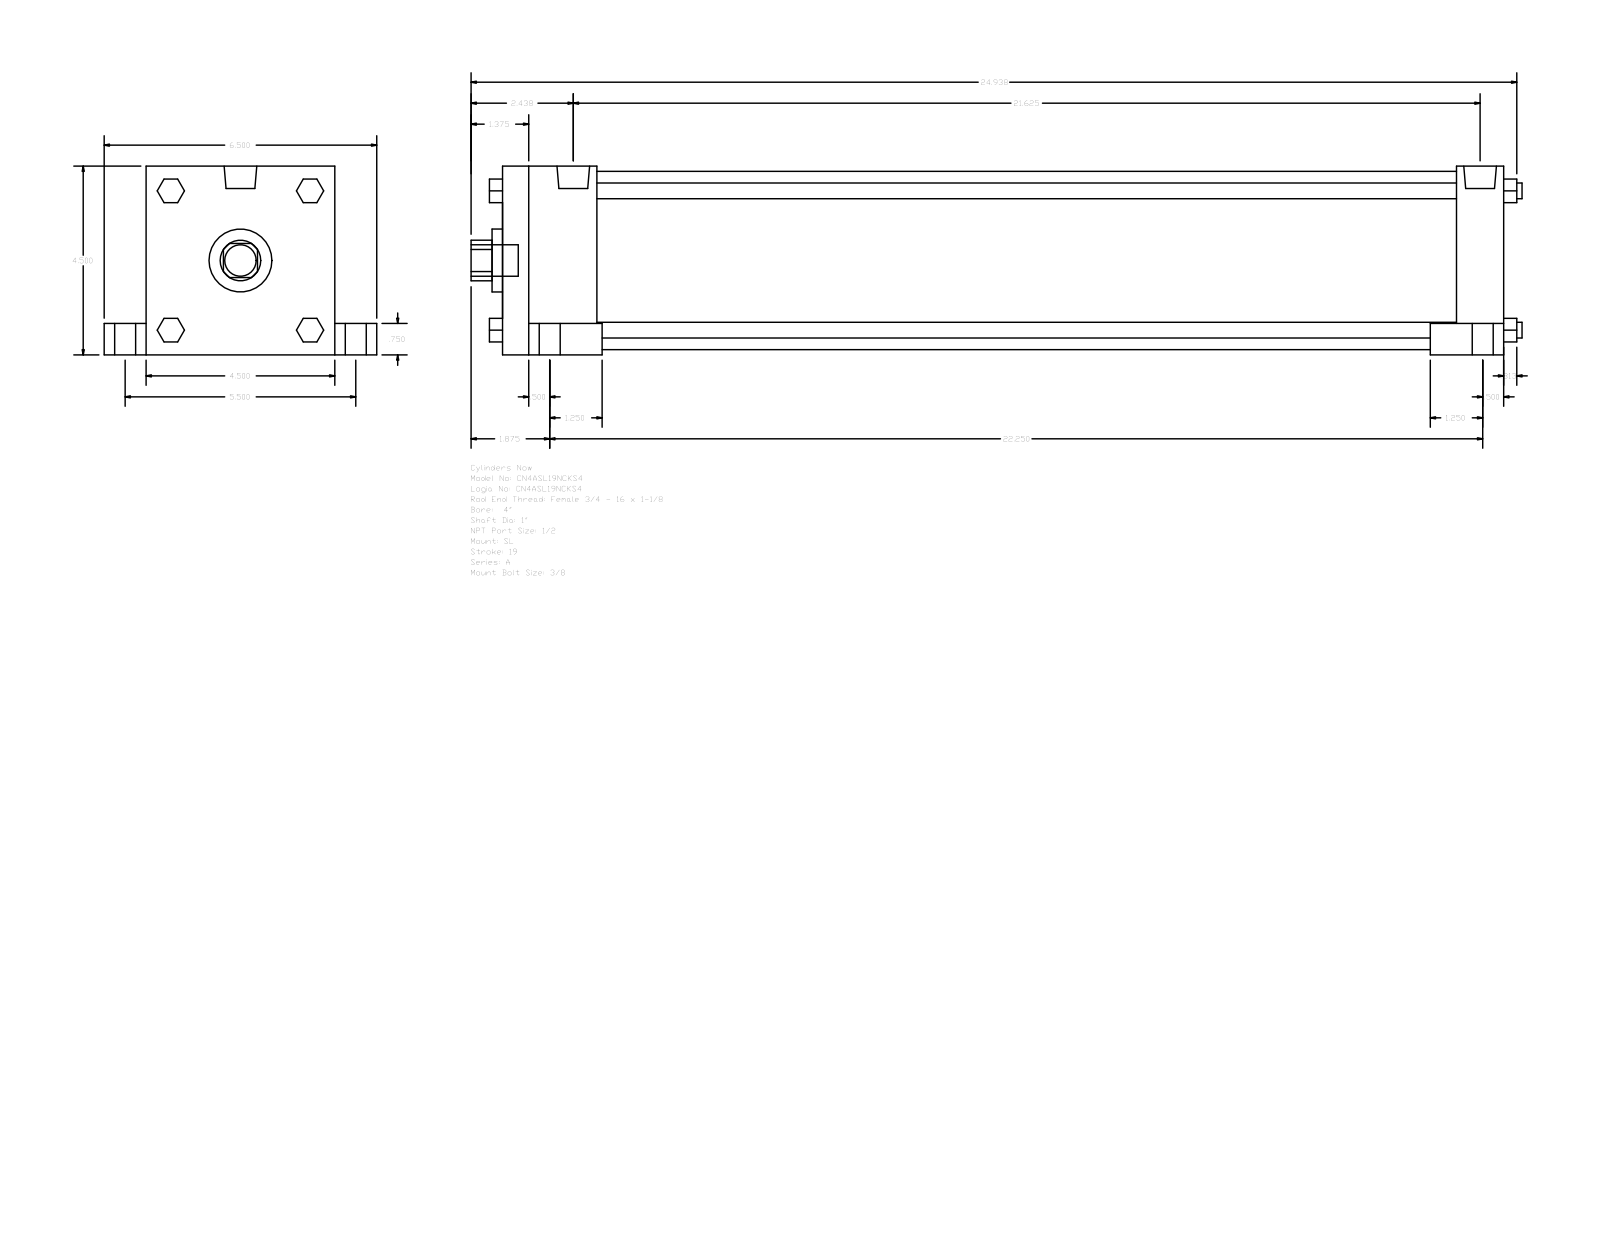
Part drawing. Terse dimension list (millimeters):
name: A_SL__0400_1
written by: GSSL Pune (CONFIG_CONTROL_DESIGN)
unit: mm
bodies: 0 solids, 150 faces (114 planar, 36 cylindrical, 0 other)
size: 636.59 × 165.1 × 114.3
holes: 1× ⌀25.4, 1× ⌀38.1, 1× ⌀107.95
bosses: 5× ⌀19.05, 4× ⌀12.7, 4× ⌀9.53, 4× ⌀8.73, 2× ⌀19.77
rounds: 1× R12.29
face distances: 114.3, 606.43, 57.15, 549.28, 577.85, 520.7, 28.58, 19.05, 25.4, 139.7
